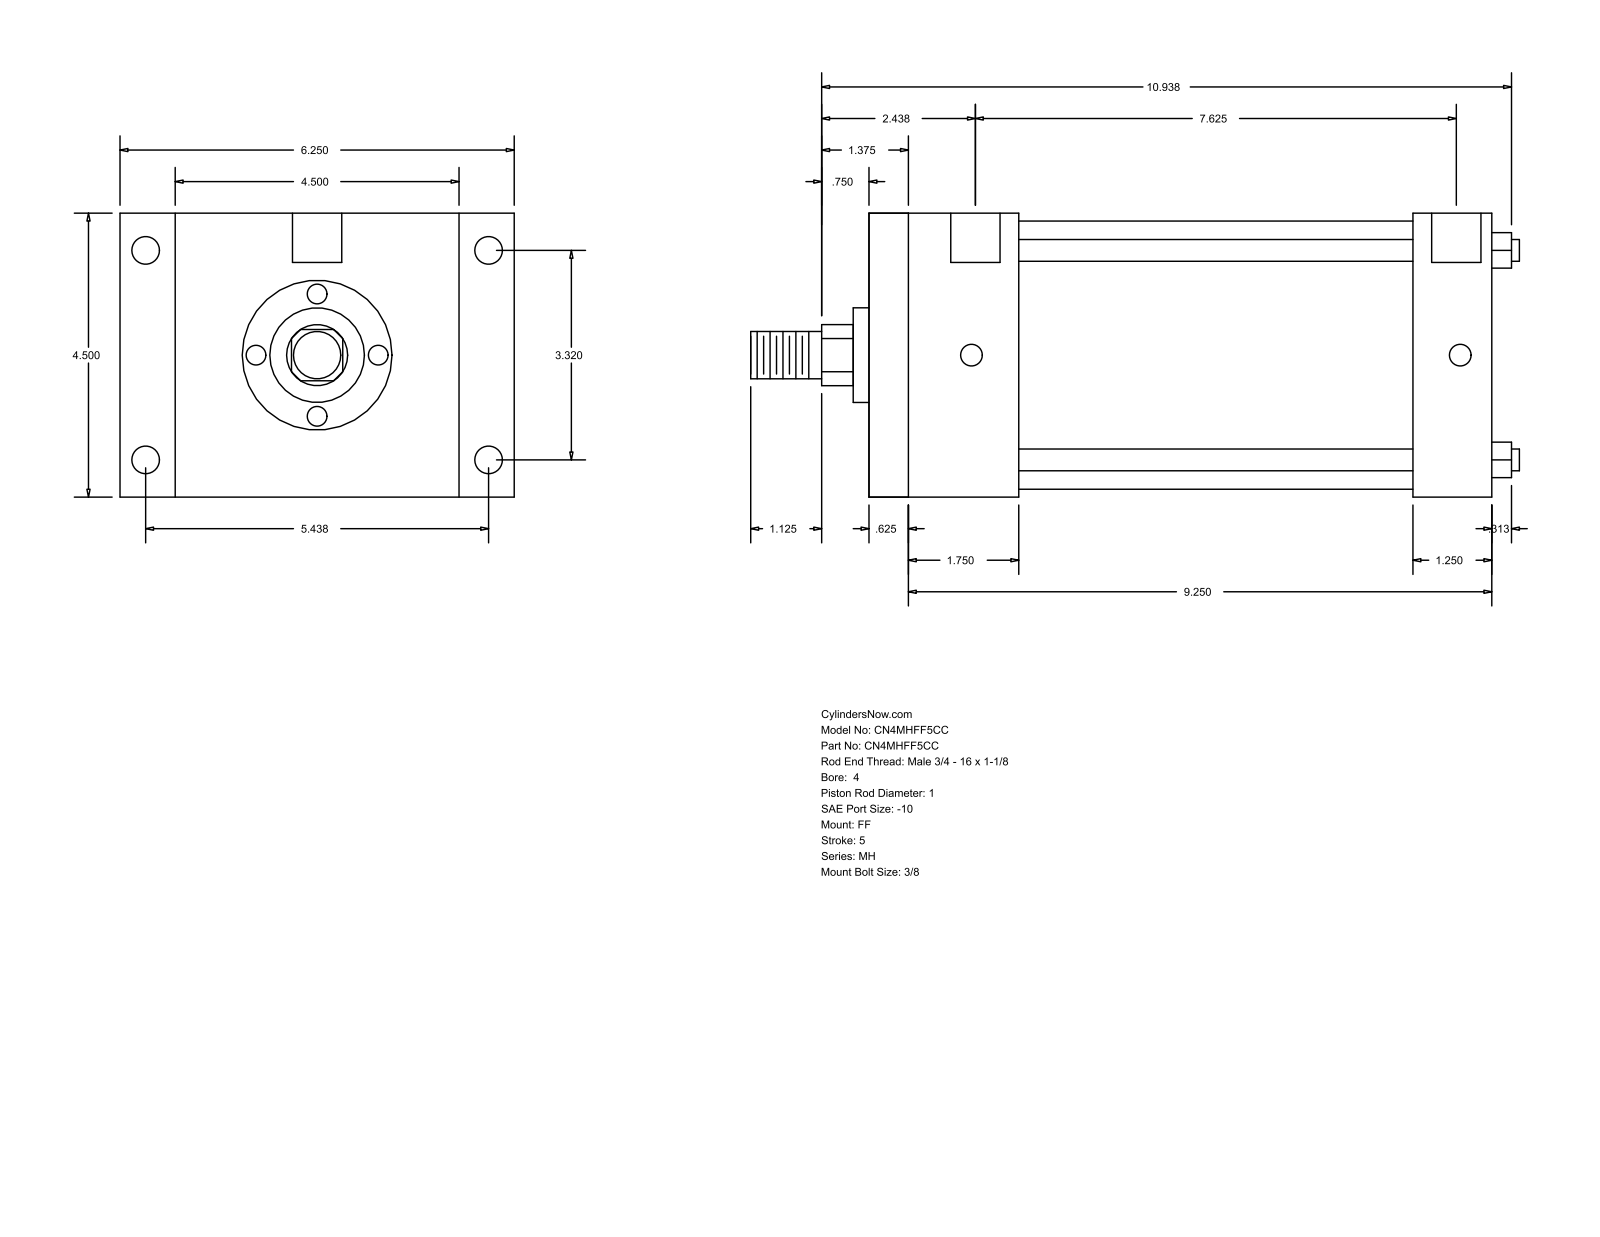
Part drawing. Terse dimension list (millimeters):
name: MH_FF__0400_1
written by: GSSL Pune (CONFIG_CONTROL_DESIGN)
unit: mm
bodies: 0 solids, 92 faces (64 planar, 28 cylindrical, 0 other)
size: 309.56 × 158.75 × 114.3
holes: 4× ⌀8.73, 4× ⌀11.13, 2× ⌀19.84
bosses: 4× ⌀8.76, 1× ⌀107.95, 1× ⌀38.1, 1× ⌀25.4, 1× ⌀19.05
rounds: 1× R12.29
face distances: 114.3, 250.83, 15.87, 234.96, 60.33, 44.46, 190.5, 219.07, 203.2, 158.74
hole spacings: 84.32, 138.12, 161.82, 196.85, 1.58, 1.59, 193.68, 195.26
